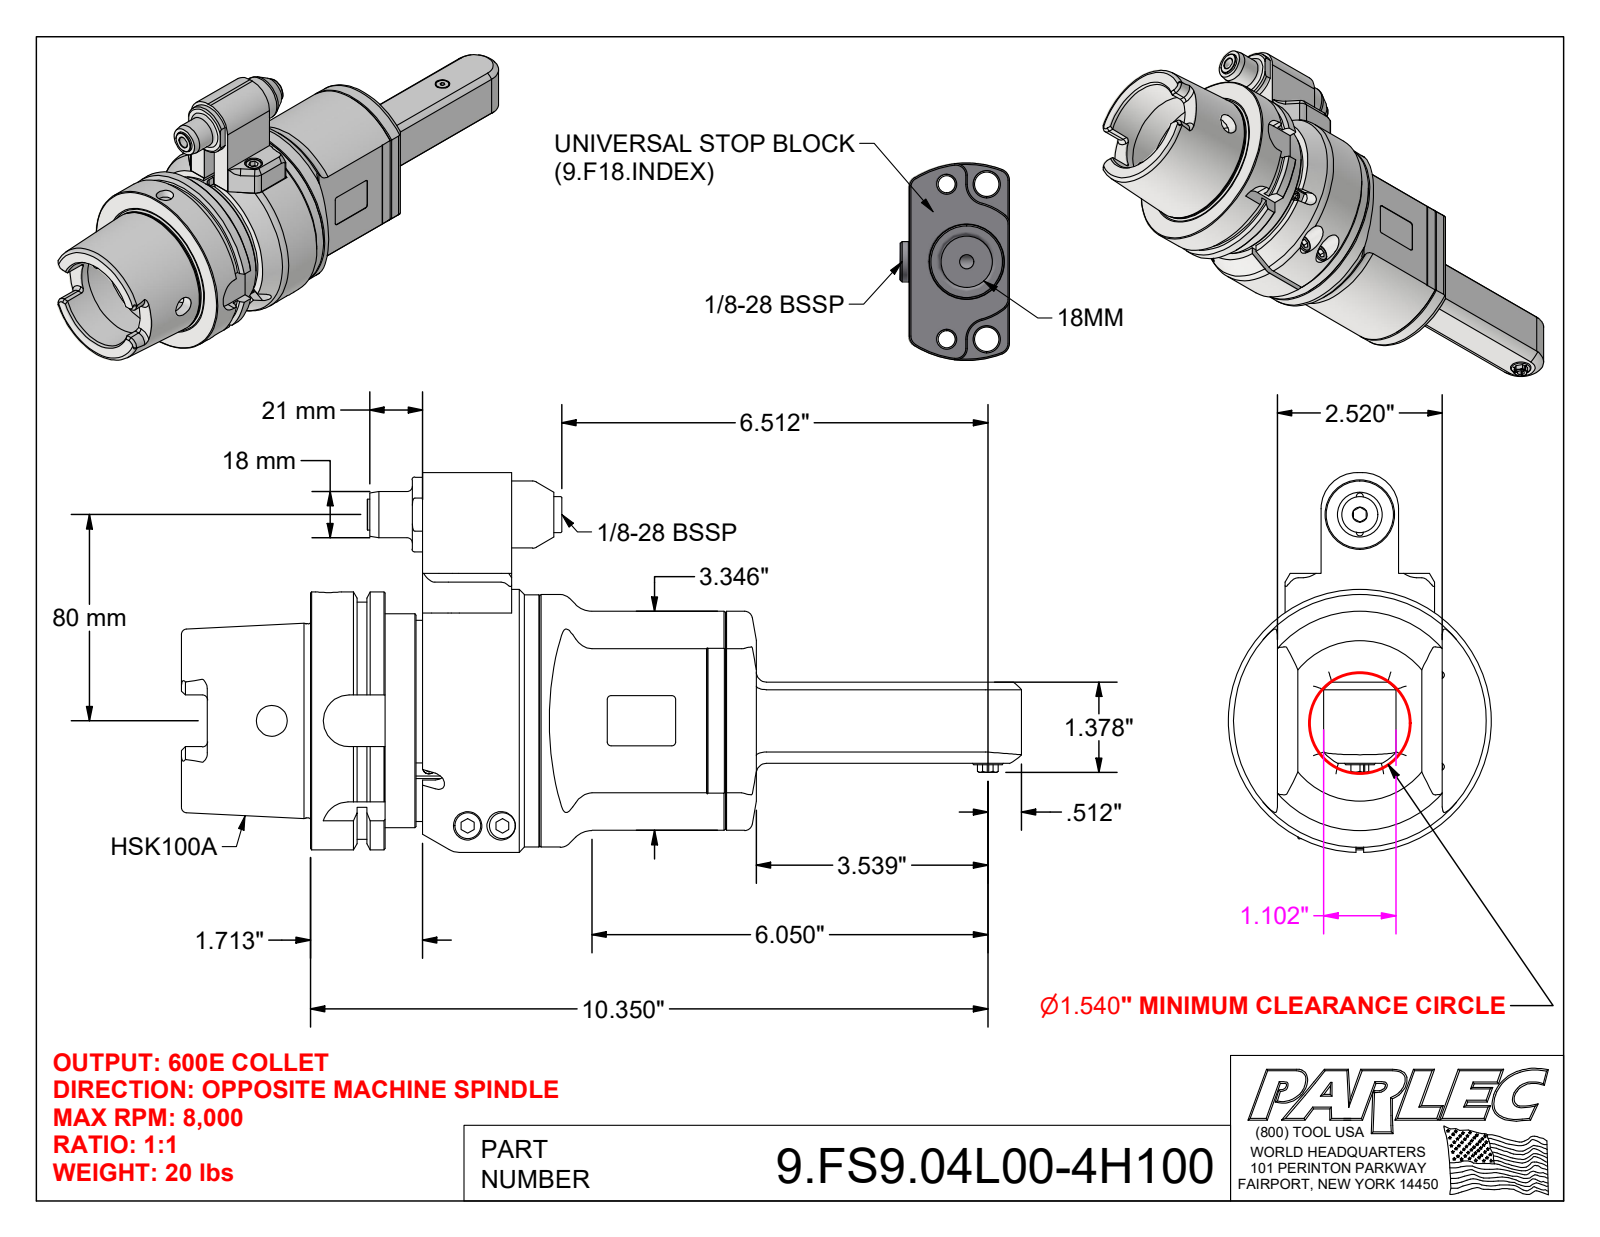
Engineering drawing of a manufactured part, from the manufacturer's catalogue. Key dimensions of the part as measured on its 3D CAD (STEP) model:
Part name (STEP PRODUCT): 9.FS9.04L00-4H100; 9_FS9_04L00; 9_GA1_518_2 (Type 1, H100A, 80mm)
STEP written by: Autodesk Inventor 2022 (AUTOMOTIVE_DESIGN)
Units: inches
Bodies: 5 solids, 512 faces (252 planar, 138 cylindrical, 122 other)
Overall size (bounding box): 12.831 × 5.796 × 4.016
Volume: 76.23 in³ · Surface area: 269.6 in²
Round holes (diameter × count): ⌀0.197 ×4, ⌀0.102 ×2, ⌀0.118 ×2, ⌀0.335 ×2, ⌀0.409 ×2, ⌀0.433 ×2, ⌀0.472 ×2, ⌀0.098 ×1, ⌀0.157 ×1, ⌀0.256 ×1, ⌀0.276 ×1, ⌀0.394 ×1
Round bosses / shafts (diameter × count): ⌀0.394 ×4, ⌀0.236 ×4, ⌀0.315 ×3, ⌀0.709 ×2, ⌀0.098 ×2, ⌀4.016 ×1, ⌀3.937 ×1, ⌀3.858 ×1
Partial cylindrical surfaces — rounded edges, fillets, slot ends (radius × count): R0.079 ×14, R0.157 ×11, R0.059 ×4, R0.192 ×4, R0.394 ×4, R0.551 ×3, R0.02 ×2, R0.039 ×2
Main face-to-face distances: 0.709, 1.142, 1.26, 0.118, 1.811, 1.89, 1.555, 1.181, 0.492, 0.039
Hole centre spacings: 0.276, 0.512, 0.551, 1.081, 1.72, 2.208, 2.652, 2.764
